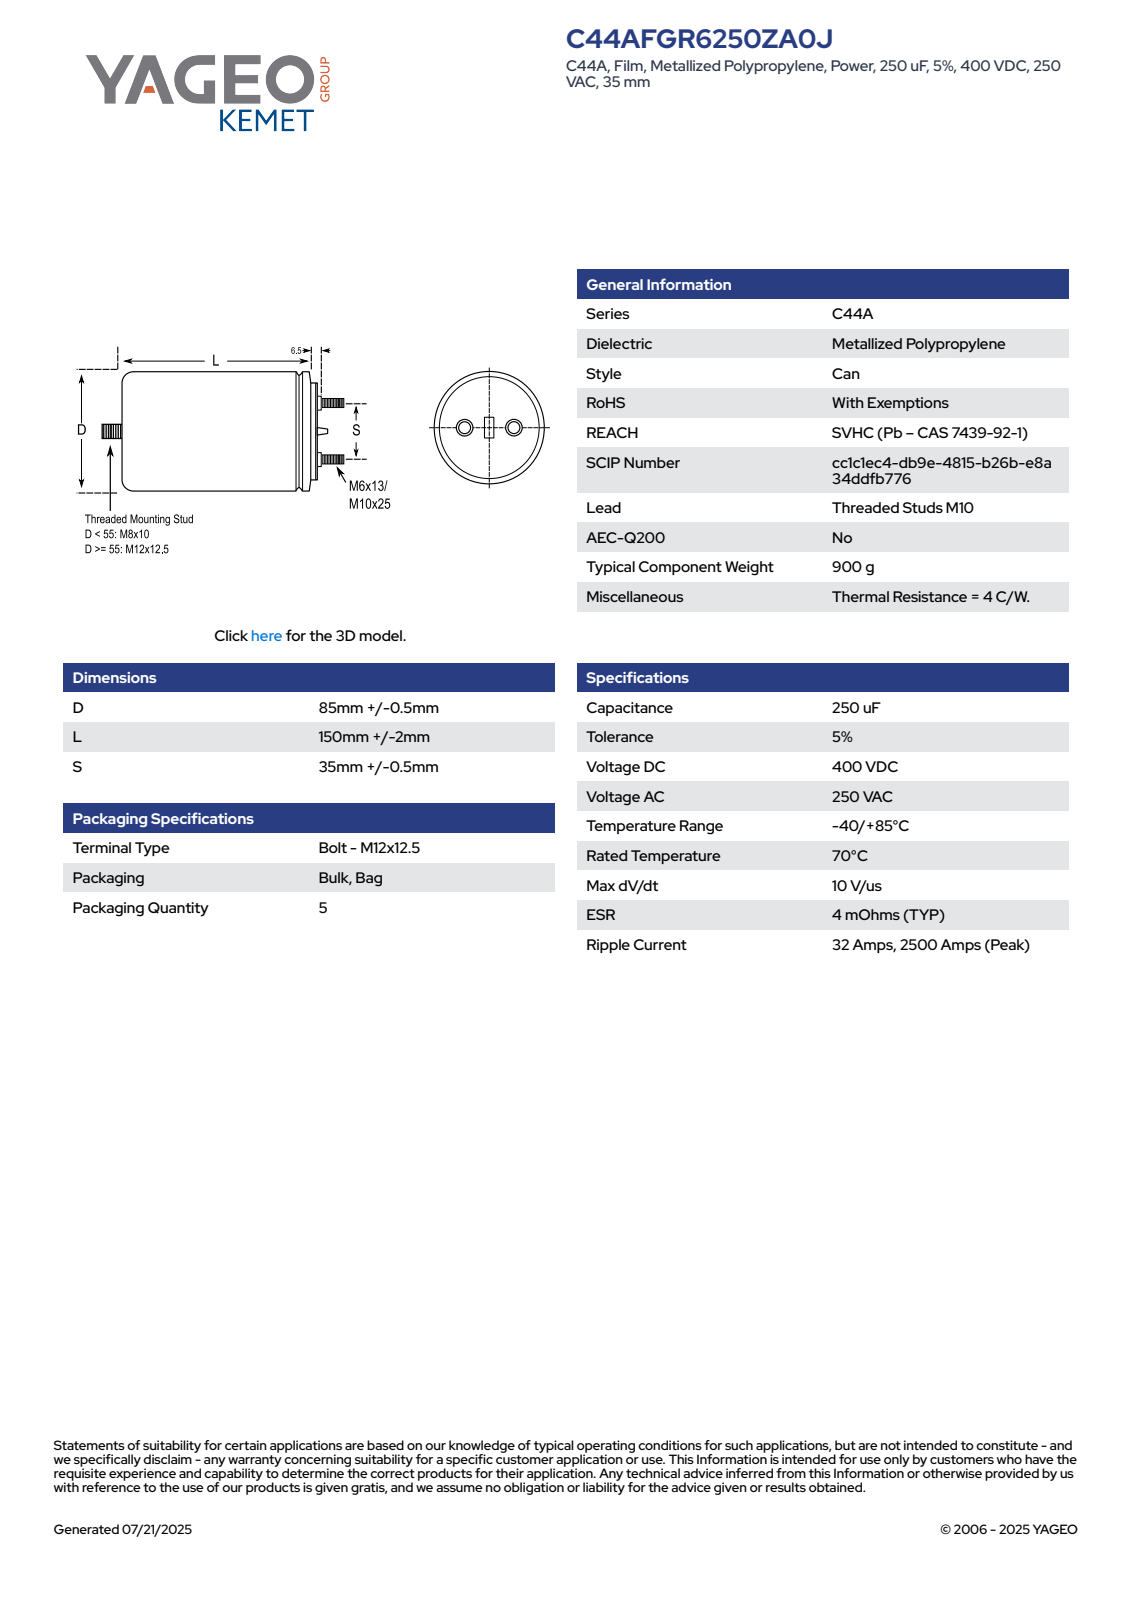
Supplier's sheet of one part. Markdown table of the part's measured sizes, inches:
| quantity | value |
| --- | --- |
| part name | CFP_C44A_85X150_D85.5L152S35 |
| STEP written by | SolidWorks 2014 (AUTOMOTIVE_DESIGN) |
| units | inches |
| bodies | 1 solid, 102 faces (29 planar, 34 cylindrical, 39 other) |
| overall size | 7.244 × 3.366 × 3.366 |
| volume | 54.06 in³ |
| surface area | 83.74 in² |
| round bosses / shafts (diameter × count) | 0.354 × 2, 0.236 × 2, 3.366 × 1, 2.64 × 1, 0.472 × 1 |
| partial cylindrical surfaces (radius × count) | 1.683 × 1 |
| main face-to-face distances | 6.181, 0.492, 6.673, 6.732, 6.24, 0.059, 7.244, 6.752, 0.571, 0.512 |
